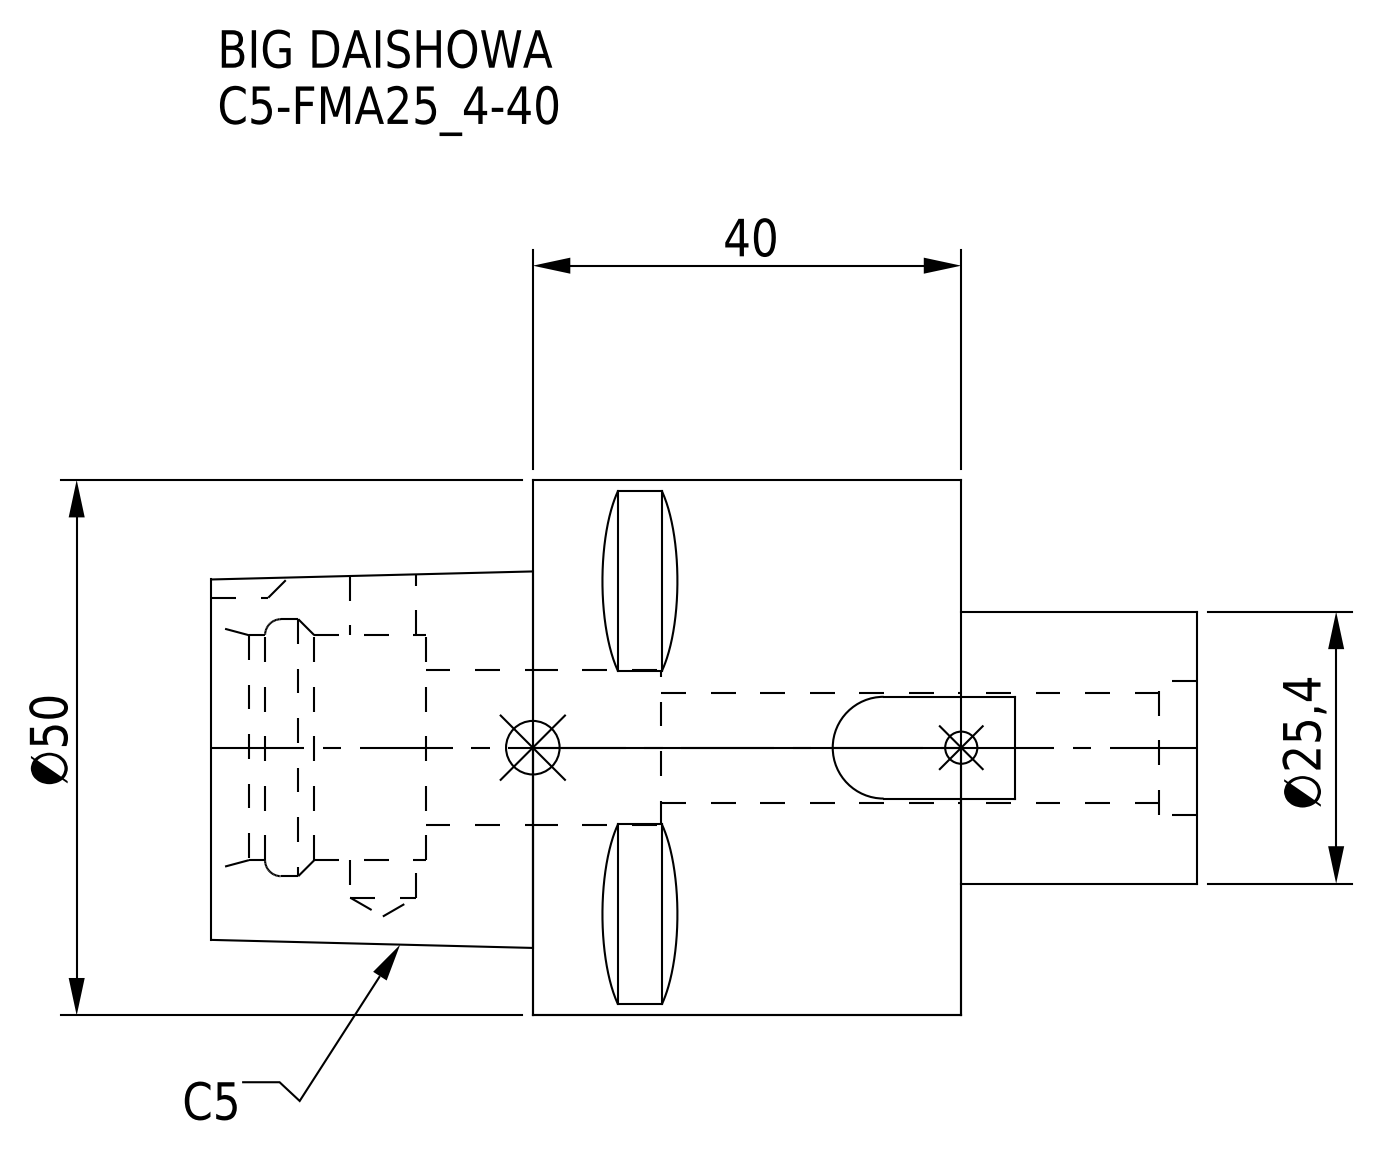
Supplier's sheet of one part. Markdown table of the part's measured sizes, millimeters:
| quantity | value |
| --- | --- |
| part name | C5-FMA25_4-40 |
| STEP written by | CREO PARAMETRIC BY PTC INC, 2016380 (AUTOMOTIVE_DESIGN) |
| units | millimeters |
| bodies | 1 solid, 70 faces (39 planar, 21 cylindrical, 10 other) |
| overall size | 92 × 50 × 50 |
| volume | 101 687 mm³ |
| surface area | 19 752 mm² |
| round holes (diameter × count) | 6.1 × 1, 10.25 × 1, 12.5 × 1, 14.5 × 1, 21 × 1, 24 × 1 |
| round bosses / shafts (diameter × count) | 50 × 1, 25.4 × 1 |
| partial cylindrical surfaces (radius × count) | 4 × 1 |
| main face-to-face distances | 40, 22, 62, 92, 70, 30, 50, 17, 5, 45 |
